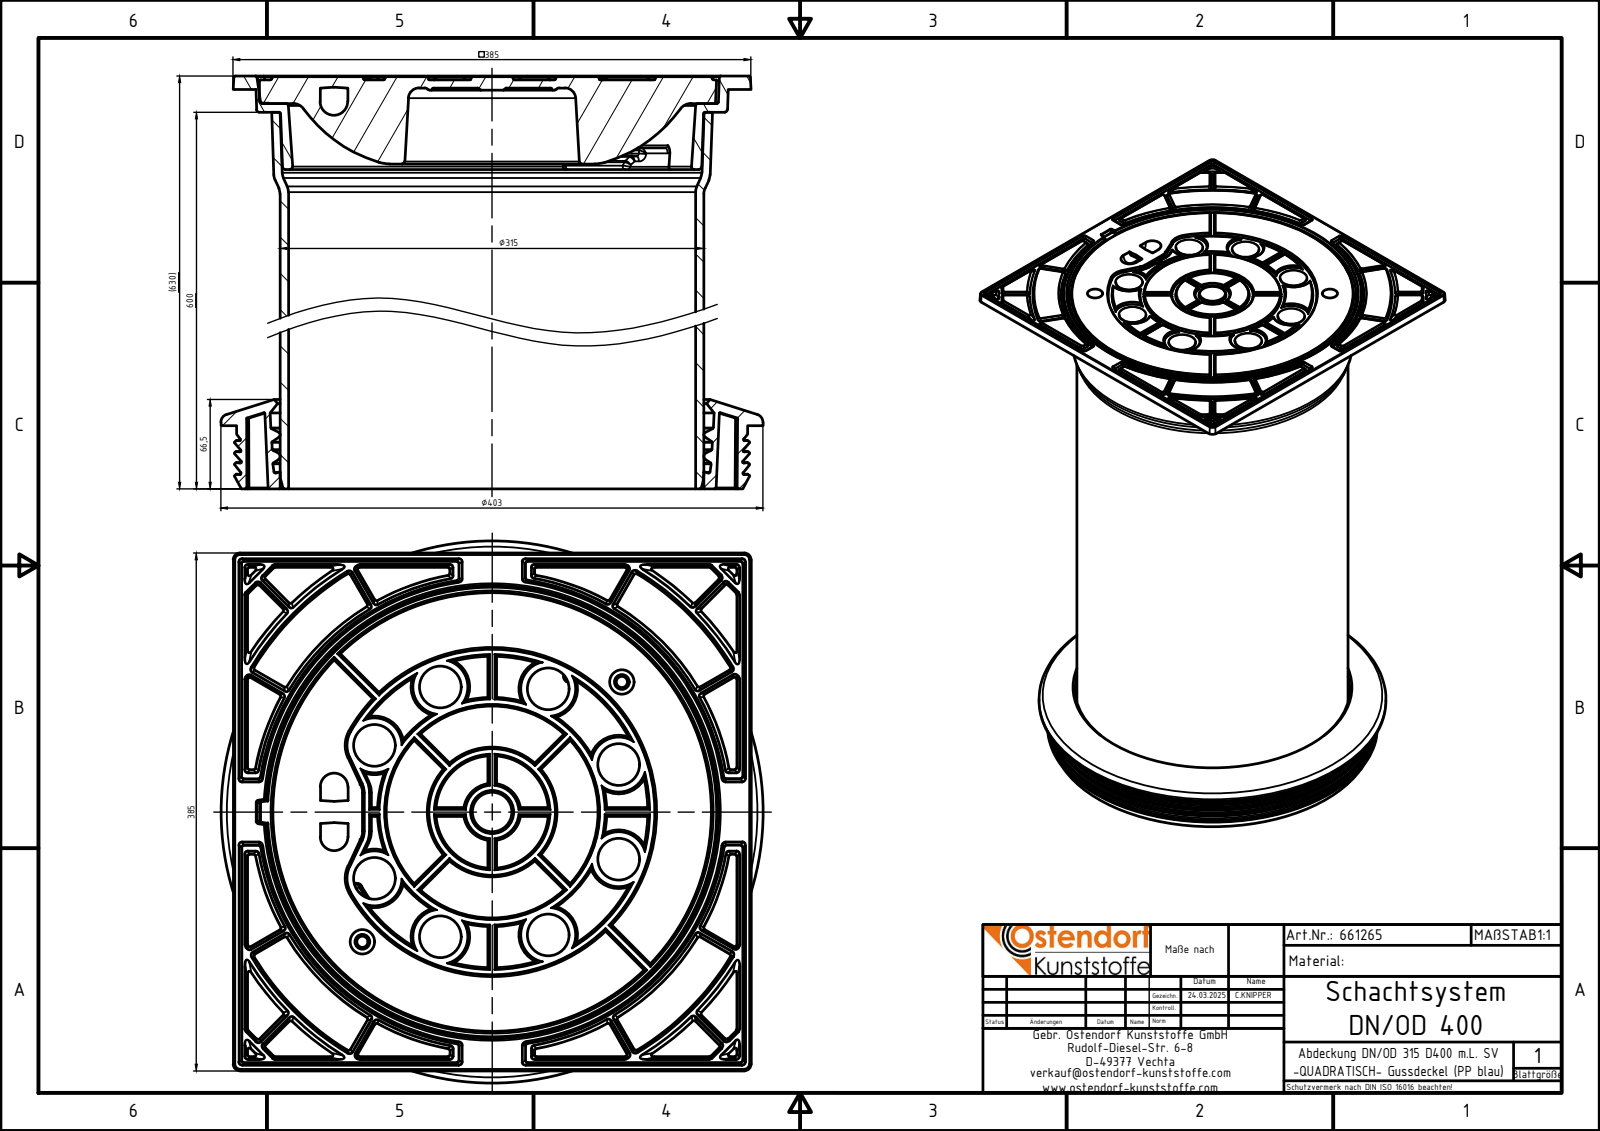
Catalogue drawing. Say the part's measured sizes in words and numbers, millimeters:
The part is named "661265z; 660300z; 660500_05.02.25z; 990050z (+1 more)". Its 3-D file was written by "Autodesk Inventor 2024 (AUTOMOTIVE_DESIGN)". It is 4 solids with 1838 faces: 245 planar, 371 cylindrical and 1222 other. Overall it measures 627 by 403 by 403 millimeters. Its volume is 8 761 000 cubic millimeters and its surface area 2 157 000 square millimeters. Round holes: 8 of diameter 31, 2 of diameter 8.38, 2 of diameter 11, 2 of diameter 18, 1 of diameter 302.6, 1 of diameter 315. Round bosses or shafts: 1 of diameter 403, 1 of diameter 380. Partial cylindrical surfaces (rounded edges, fillets, slot ends): 208 of radius 1, 48 of radius 2.5, 18 of radius 0.5, 8 of radius 4, 4 of radius 2, 1 of radius 3. The main face-to-face distances are 9.5, 0.5, 10, 10.5, 20.5, 20, 6.5, 17, 26.5, 27. The hole center spacings are 100.5, 65.44, 76.92, 80.14, 100.49, 135.79, 137.08, 144.58.
